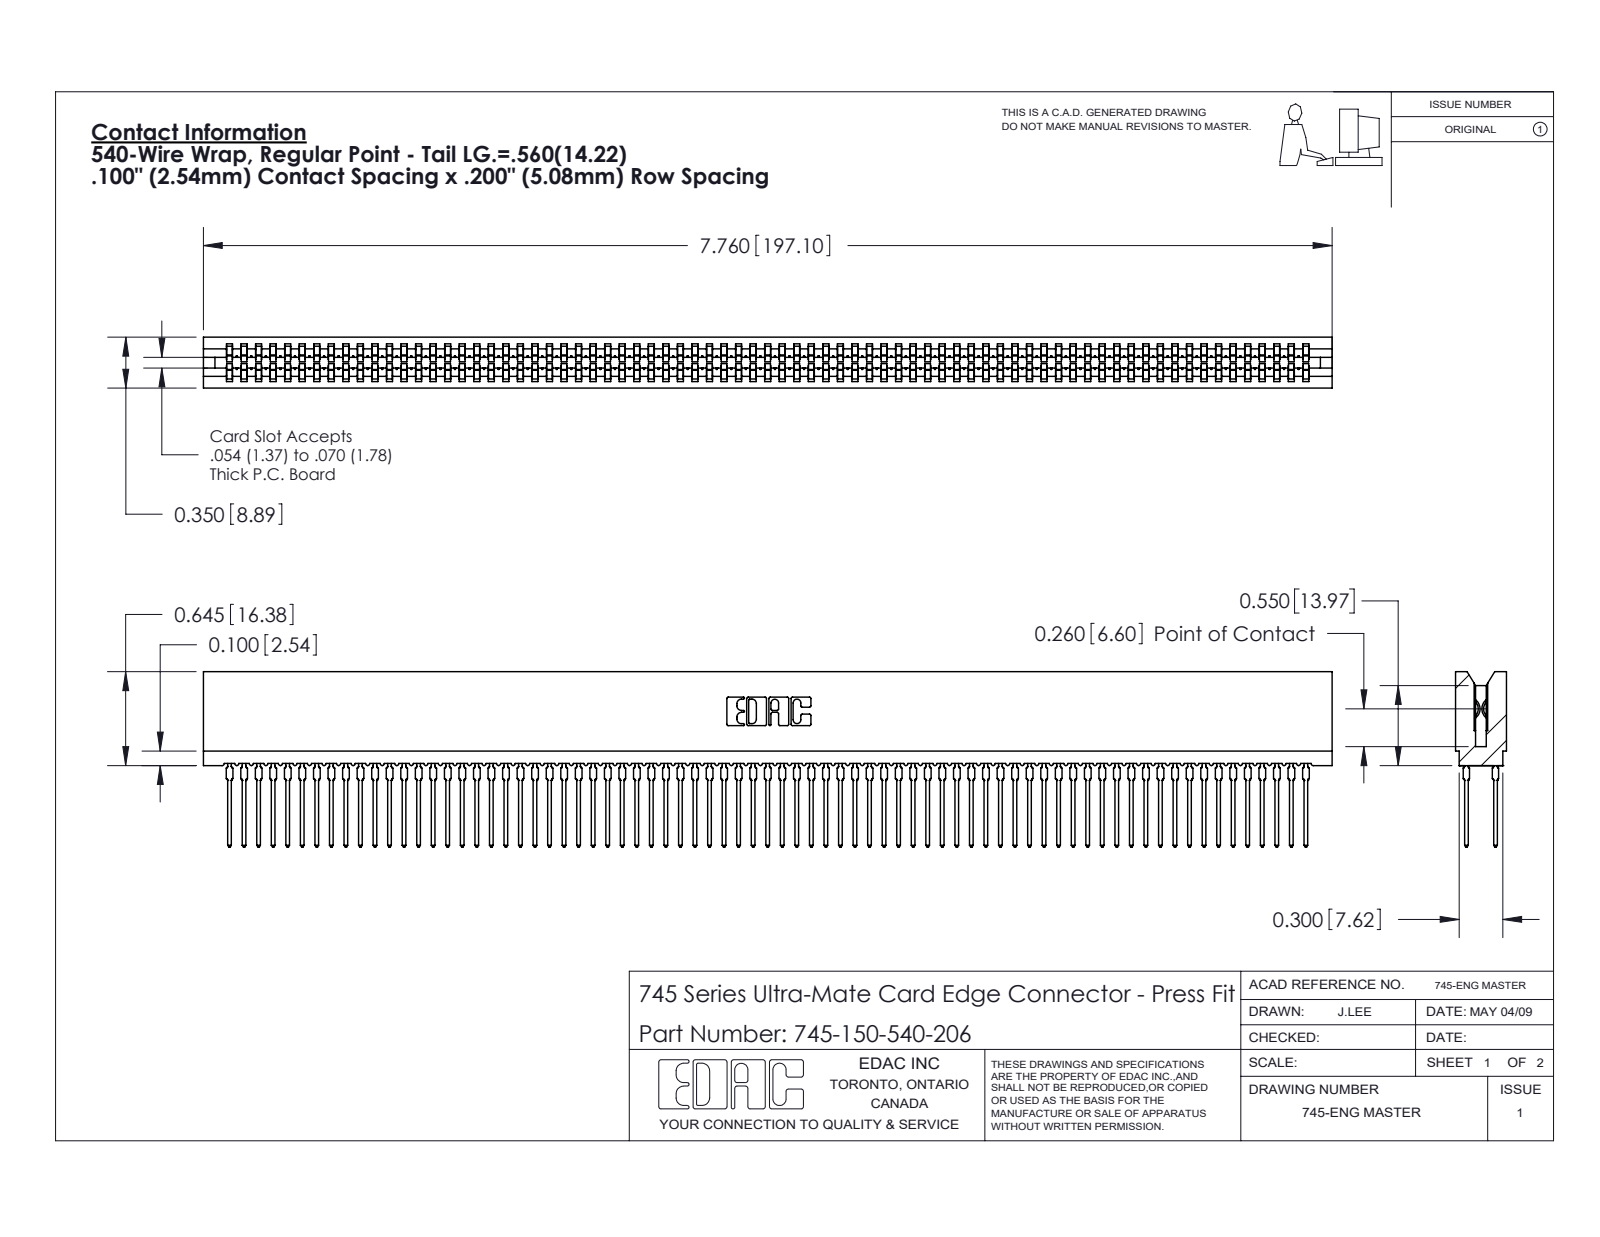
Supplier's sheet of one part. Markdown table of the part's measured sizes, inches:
| quantity | value |
| --- | --- |
| part name | 745-150-540-206; 745-292-001_540; 745 Part_Insulator Option - 06 |
| STEP written by | SolidWorks 2020 (CONFIG_CONTROL_DESIGN) |
| units | inches |
| bodies | 151 solids, 13521 faces (6956 planar, 2665 cylindrical, 3900 other) |
| overall size | 7.76 × 1.206 × 0.35 |
| volume | 1.097 in³ |
| surface area | 60.54 in² |
| partial cylindrical surfaces (radius × count) | 0.021 × 300, 0.015 × 150, 0.01 × 22, 0.005 × 8, 0.011 × 8, 0.007 × 6, 0.031 × 6, 0.026 × 3 |
| main face-to-face distances | 0.063, 0.287, 0.35, 0.045, 0.305, 0.018, 0.243, 0.2, 0.138, 0.212 |
